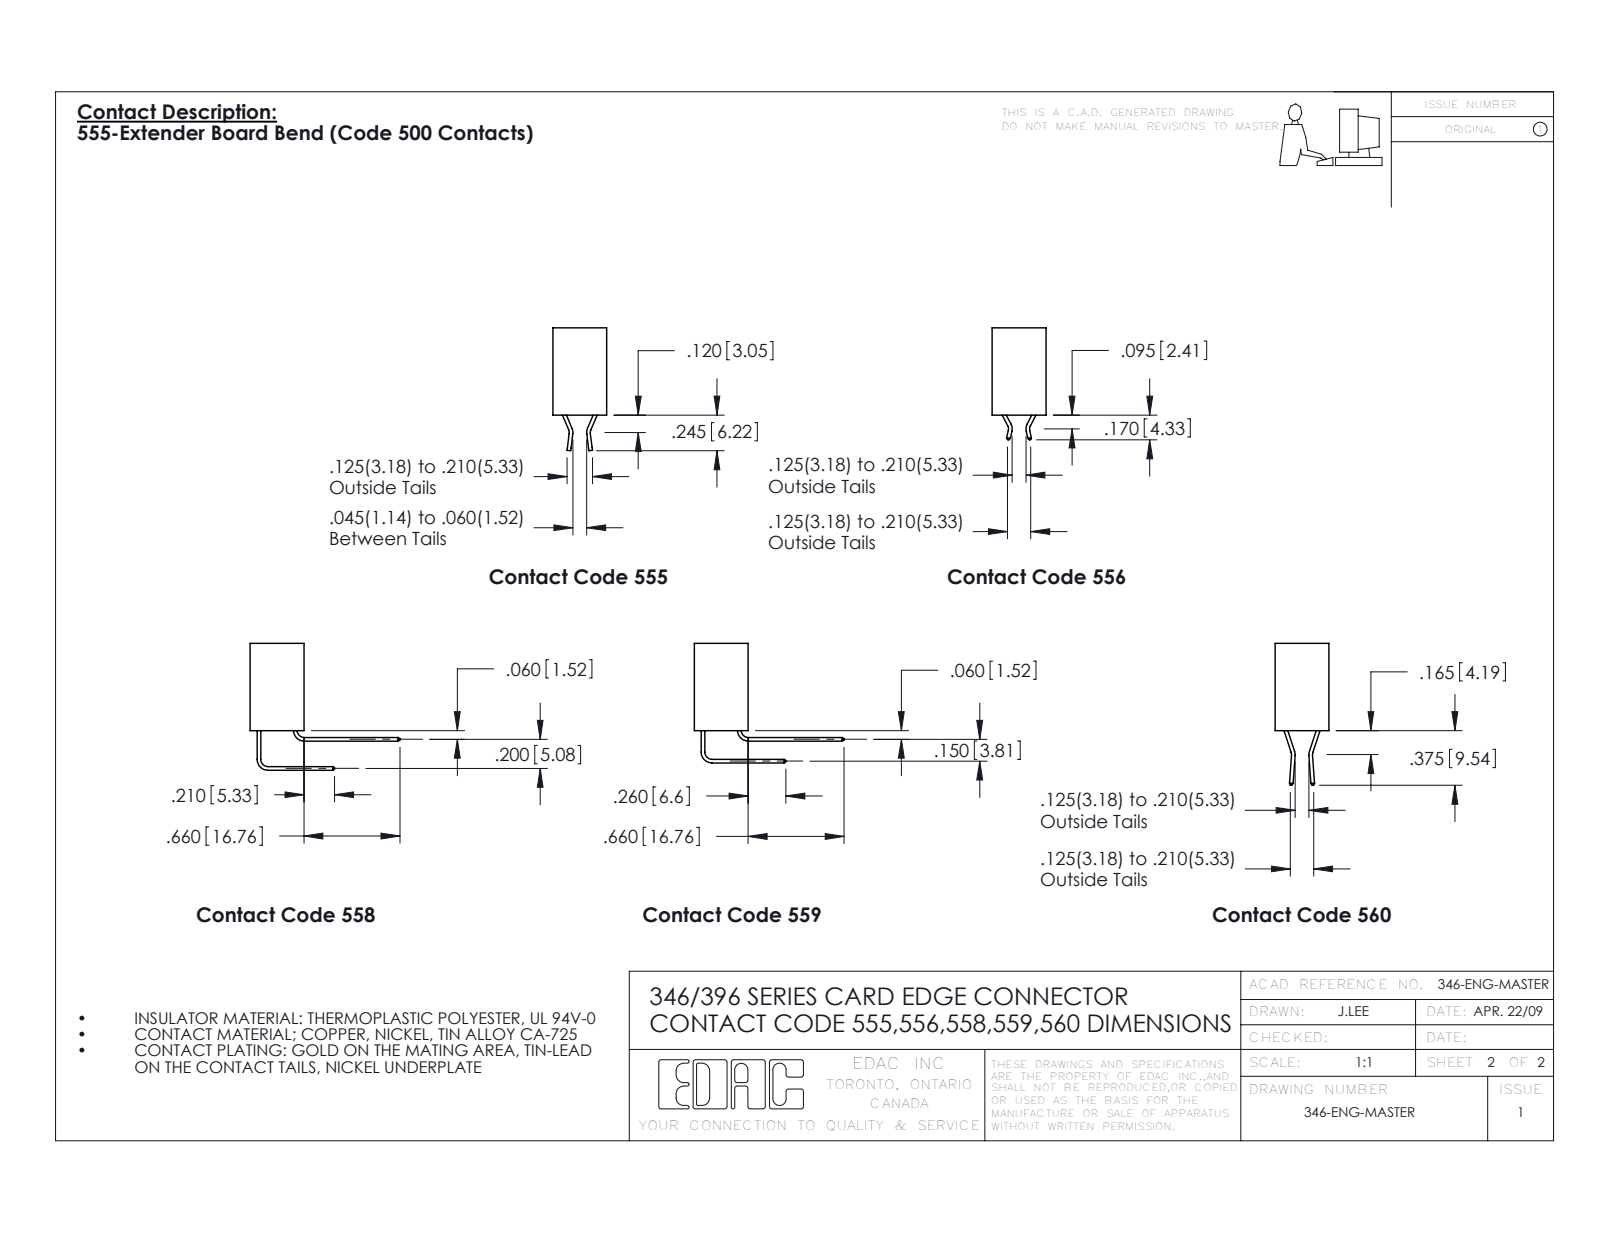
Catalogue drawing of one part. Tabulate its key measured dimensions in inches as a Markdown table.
| quantity | value |
| --- | --- |
| part name | 346 Part_No Mounting Lugs; 345-292-001_558 559 Tail - 1; 396-009-559-101 |
| STEP written by | SolidWorks 2016 (CONFIG_CONTROL_DESIGN) |
| units | inches |
| bodies | 10 solids, 654 faces (450 planar, 204 cylindrical, 0 other) |
| overall size | 1.41 × 1.03 × 0.673 |
| volume | 0.231 in³ |
| surface area | 7.165 in² |
| round holes (diameter × count) | 0.064 × 1 |
| partial cylindrical surfaces (radius × count) | 0.01 × 22, 0.006 × 18, 0.007 × 6, 0.031 × 6, 0.026 × 3, 0.031 × 2, 0.04 × 2, 0.014 × 1 |
| main face-to-face distances | 0.25, 0.048, 0.322, 0.37, 0.5, 0.072, 0.025, 0.125, 0.185, 0.065 |
